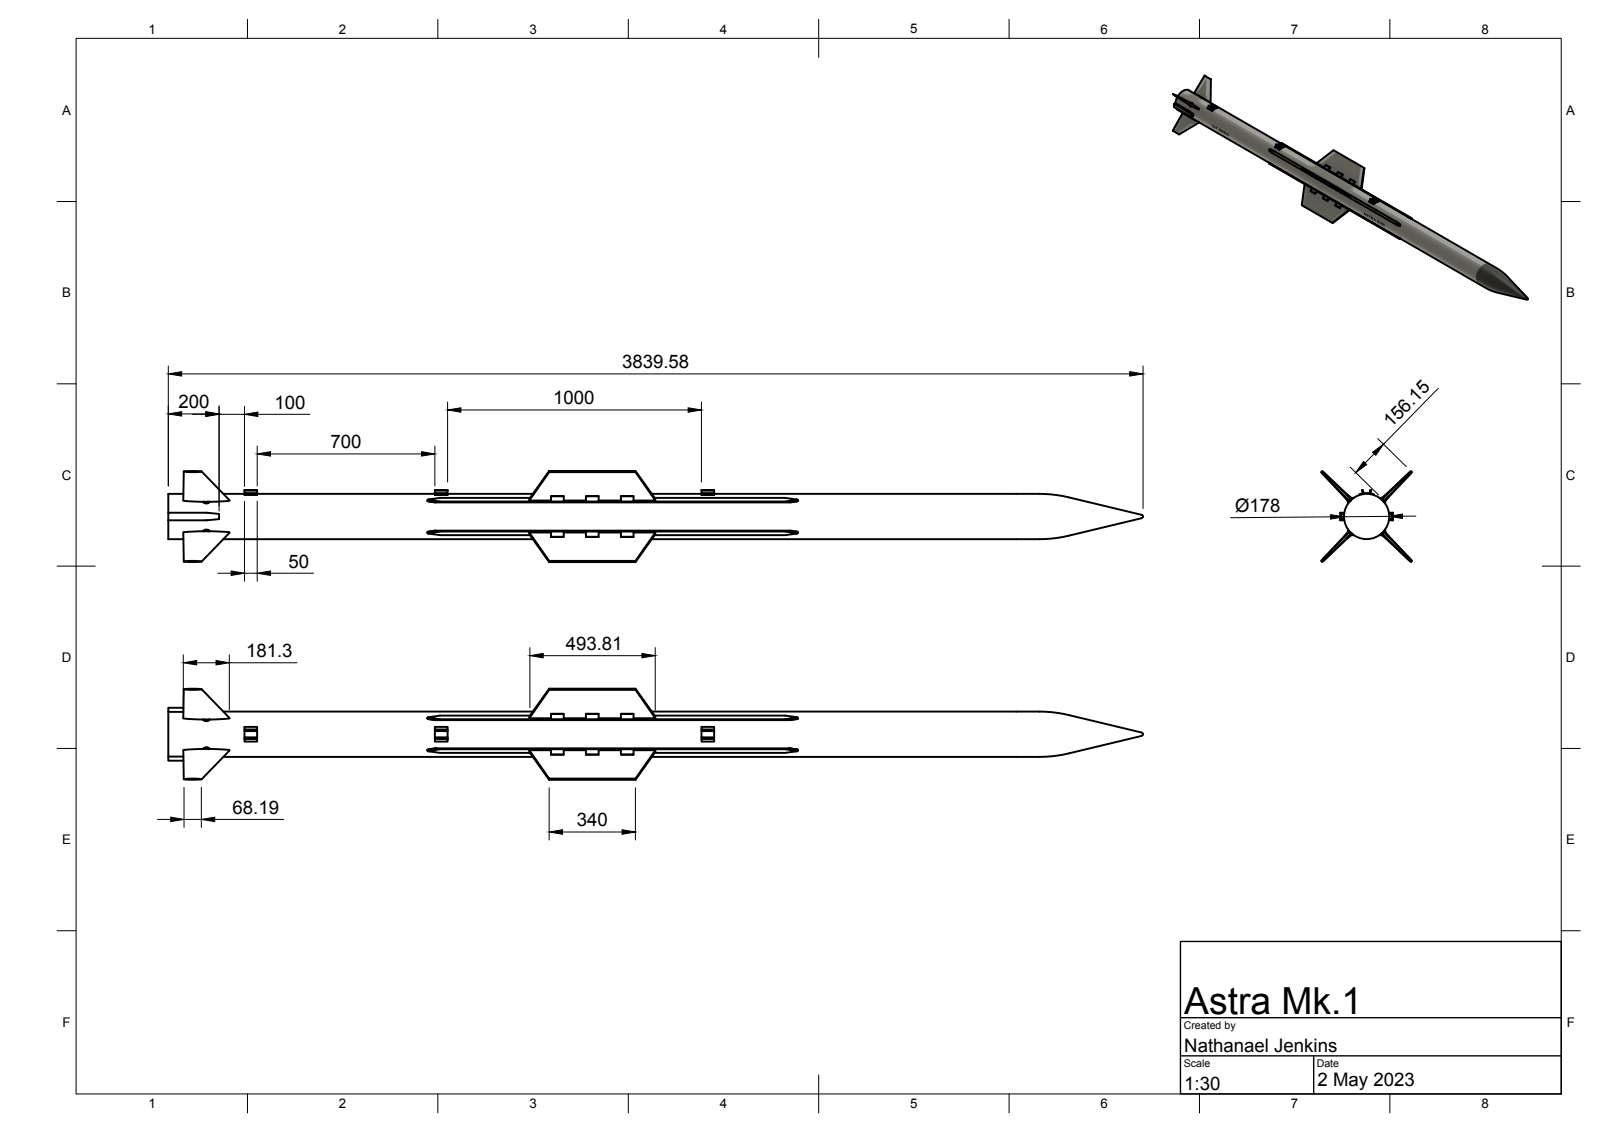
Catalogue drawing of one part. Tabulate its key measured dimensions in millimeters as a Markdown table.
| quantity | value |
| --- | --- |
| part name | Astra Mk1 v9; Missile; Launcher |
| STEP written by | Autodesk Translation Framework v12.4.0.73 (AUTOMOTIVE_DESIGN) |
| units | millimeters |
| bodies | 2 solids, 578 faces (344 planar, 135 cylindrical, 99 other) |
| overall size | 3839.57 × 526.18 × 358.36 |
| volume | 146 300 000 mm³ |
| surface area | 4 705 000 mm² |
| round holes (diameter × count) | 50 × 2, 40 × 1, 158 × 1 |
| round bosses / shafts (diameter × count) | 10 × 40, 178 × 1 |
| partial cylindrical surfaces (radius × count) | 89 × 12, 100 × 3, 10 × 2, 30 × 1, 92 × 1, 372.58 × 1 |
| main face-to-face distances | 3, 83, 86, 80, 250, 20, 63, 10, 23, 60 |
| hole center spacings | 210, 1100 |
